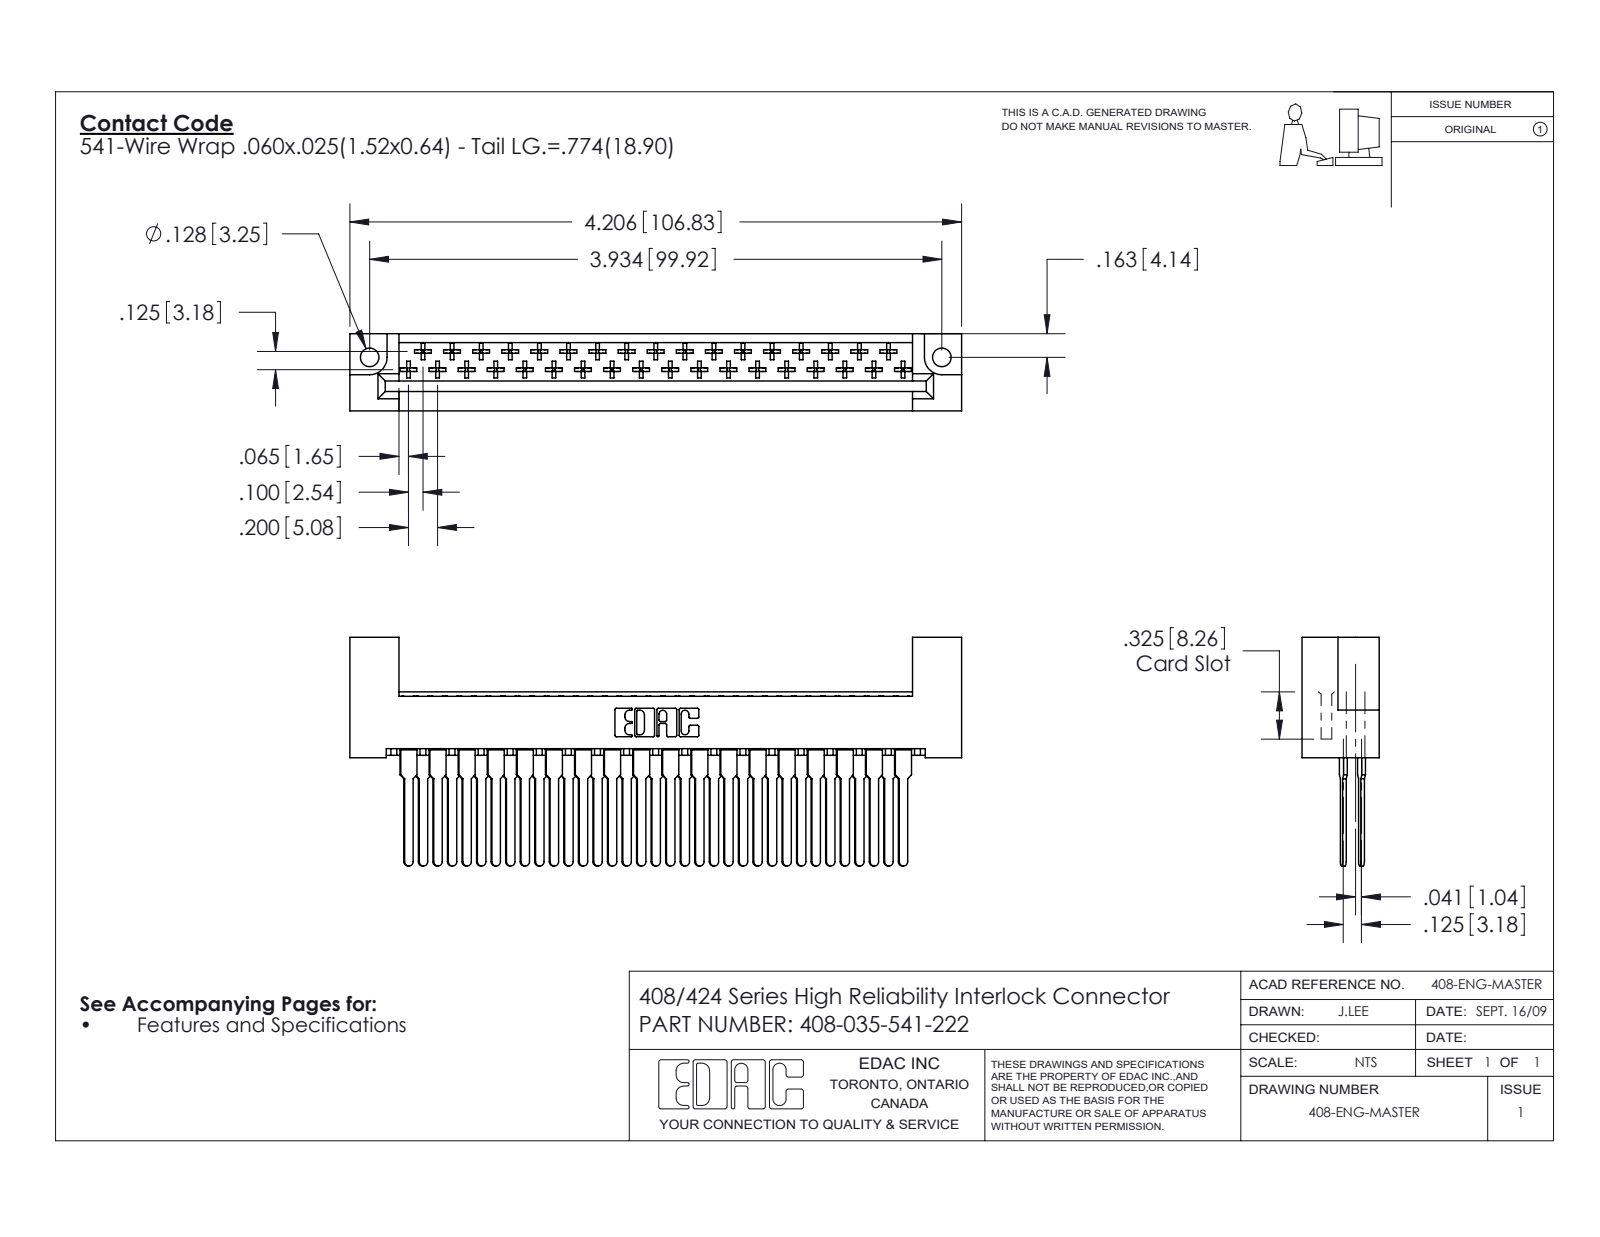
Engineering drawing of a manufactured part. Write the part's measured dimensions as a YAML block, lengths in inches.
part_name: "408 Part_035 - 2; 408-290-001_408-290-141; 408-035-541-222"
step_written_by: "SolidWorks 2016 (CONFIG_CONTROL_DESIGN)"
units: inches
bodies: {solids: 36, faces: 1994, planar: 1489, cylindrical: 365, other: 140}
overall_size: [4.206, 1.572, 0.531]
volume: 0.853
surface_area: 27.93
round_holes:
  - {diameter: 0.128, count: 2}
partial_cylinders:
  - {radius: 0.01, count: 210}
  - {radius: 0.02, count: 37}
  - {radius: 0.03, count: 35}
  - {radius: 0.01, count: 22}
  - {radius: 0.007, count: 6}
  - {radius: 0.031, count: 6}
  - {radius: 0.026, count: 3}
  - {radius: 0.12, count: 2}
face_to_face_distances: [0.531, 0.125, 0.1, 0.025, 0.025, 0.361, 0.235, 0.259, 0.272, 0.217]
hole_center_spacings: [3.934]
